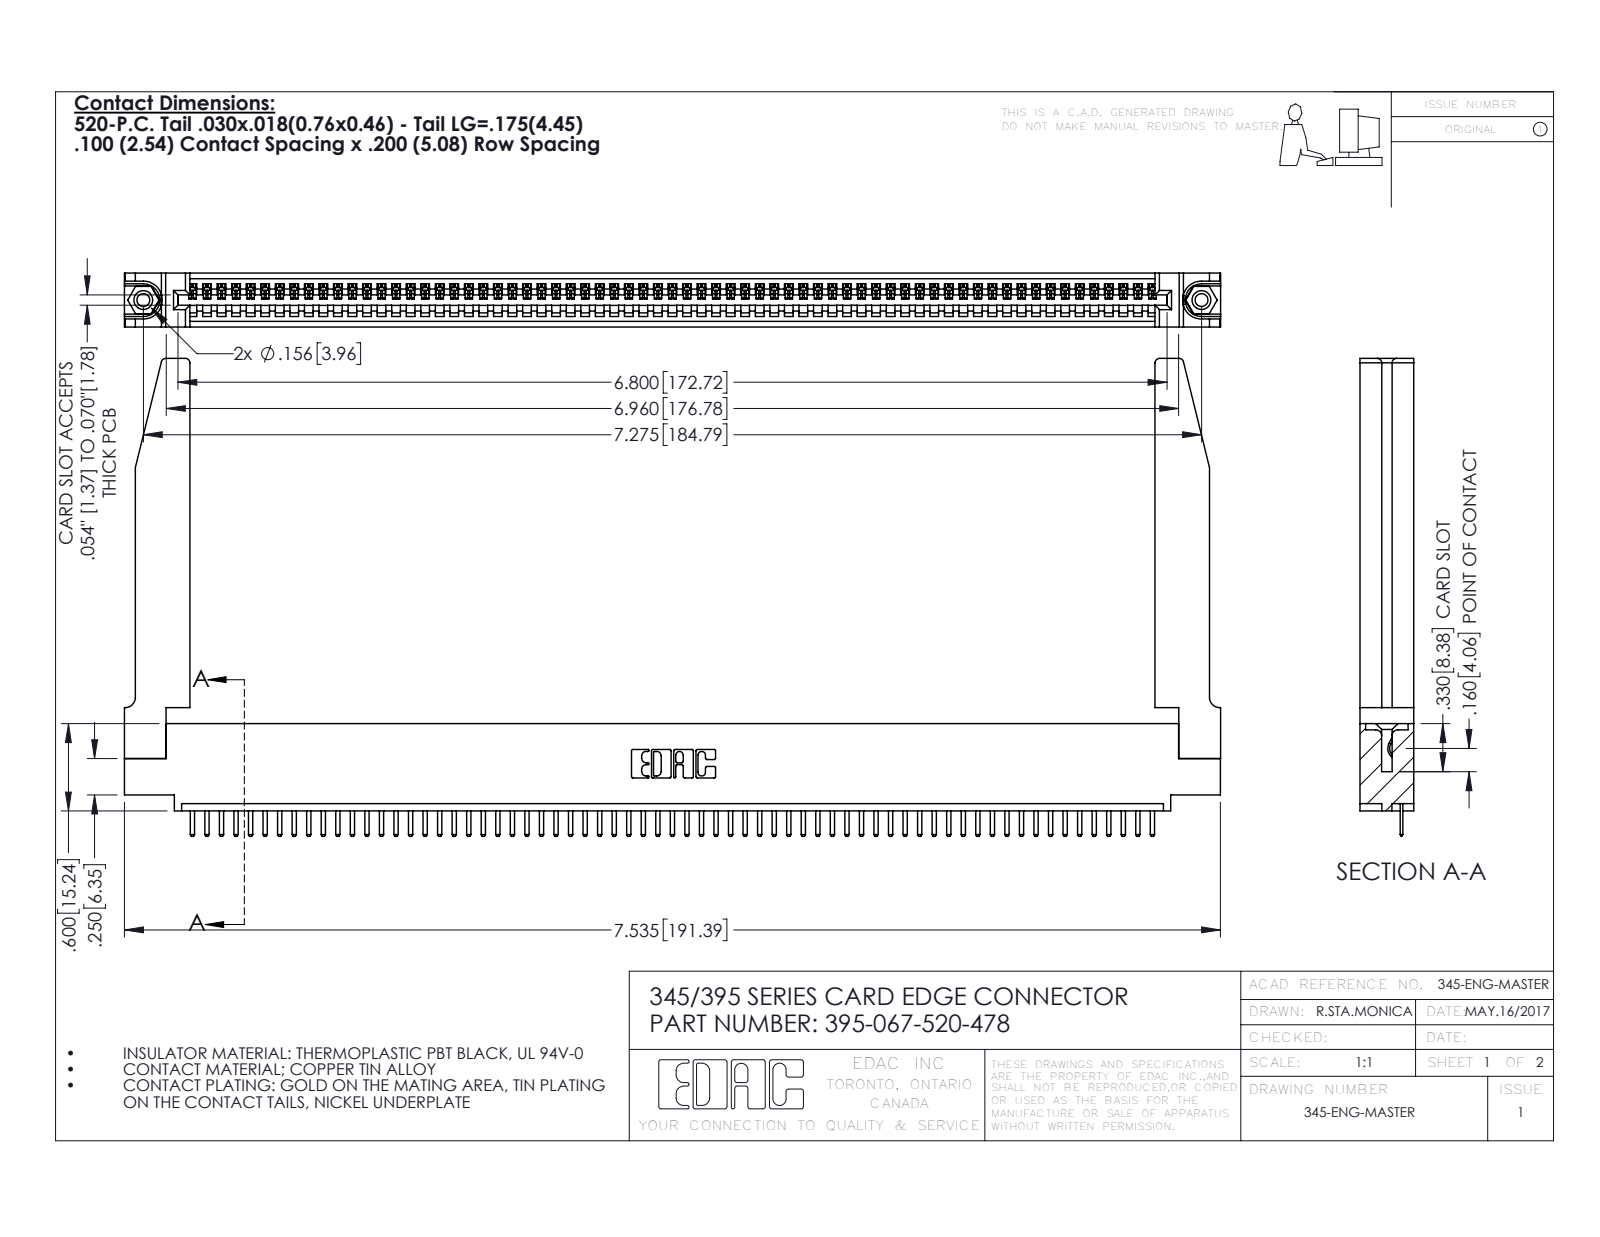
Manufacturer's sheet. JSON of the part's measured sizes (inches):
{"part_name": "345-220-078_345-220-078; 345-250-001_345-250-001-102; 345-292-001_345-293-120; 395-067-520-478 (+1 more)", "step_written_by": "SolidWorks 2016 (CONFIG_CONTROL_DESIGN)", "units": "inches", "bodies": {"solids": 72, "faces": 4518, "planar": 3040, "cylindrical": 1426, "other": 52}, "overall_size": [7.536, 3.285, 0.37], "volume_in3": 1.58, "surface_area_in2": 47.61, "round_holes": [[0.089, 2], [0.125, 2], [0.156, 2], [0.064, 1]], "round_bosses_or_shafts": [[0.155, 2]], "partial_cylinders_radius": [[0.01, 136], [0.006, 134], [0.01, 22], [0.03, 8], [0.007, 6], [0.031, 6], [0.026, 3], [0.031, 2]], "face_to_face_distances": [0.37, 0.072, 0.298, 0.098, 0.272, 0.025, 0.2, 0.225, 0.072, 0.149], "hole_center_spacings": [0.27, 7.039, 7.275]}
